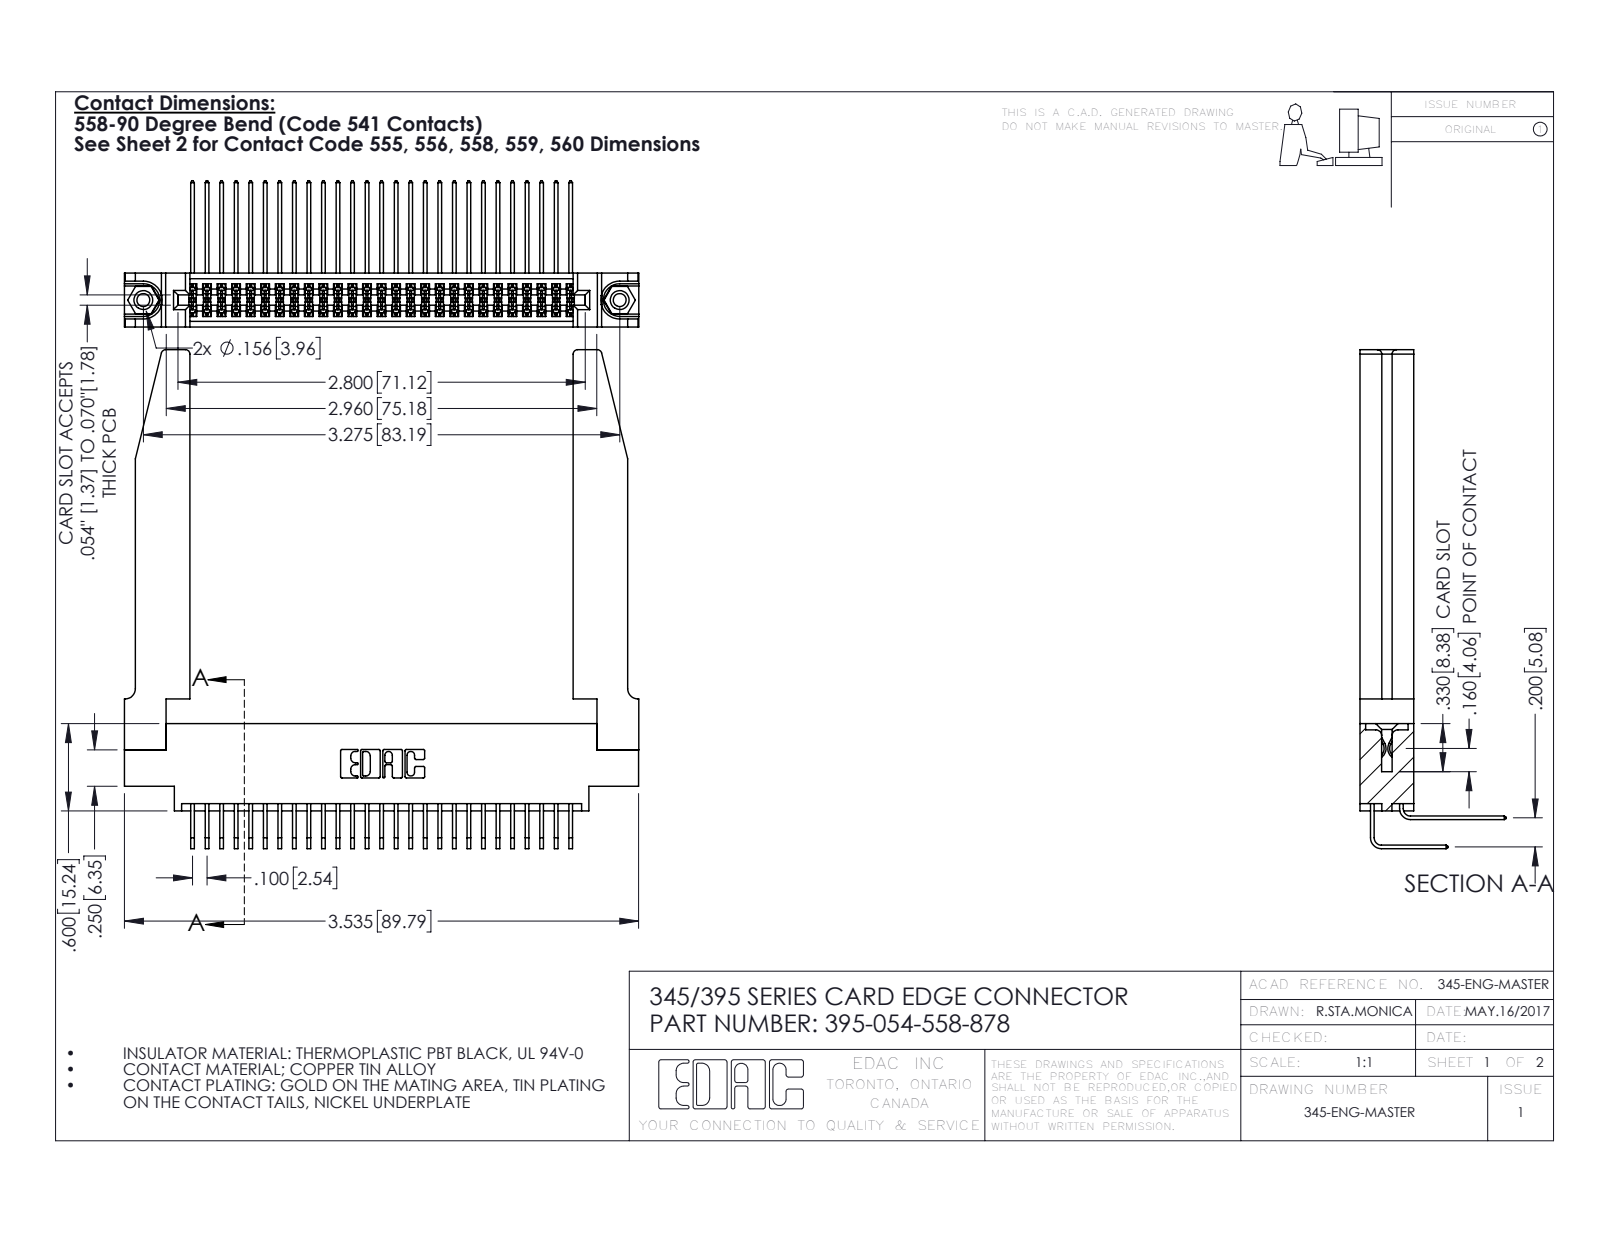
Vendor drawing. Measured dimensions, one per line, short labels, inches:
name: 345-292-001_558 Tail - 2; 345-220-078_345-220-078; 395-054-558-878; 345-250-001_345-250-001-102 (+2 more)
written by: SolidWorks 2016 (CONFIG_CONTROL_DESIGN)
unit: in
bodies: 59 solids, 3172 faces (2116 planar, 1004 cylindrical, 52 other)
size: 3.536 × 3.429 × 1.005
volume: 1.01 in³; area: 32.77 in²
holes: 2× ⌀0.089, 2× ⌀0.125, 2× ⌀0.156, 1× ⌀0.064
bosses: 2× ⌀0.155
rounds: 82× R0.006, 22× R0.01, 8× R0.03, 6× R0.007, 6× R0.031, 3× R0.026, 2× R0.014, 2× R0.019
face distances: 0.37, 0.072, 0.298, 0.2, 0.098, 0.272, 0.025, 0.225, 0.148, 0.15
hole spacings: 0.27, 3.04, 3.275
